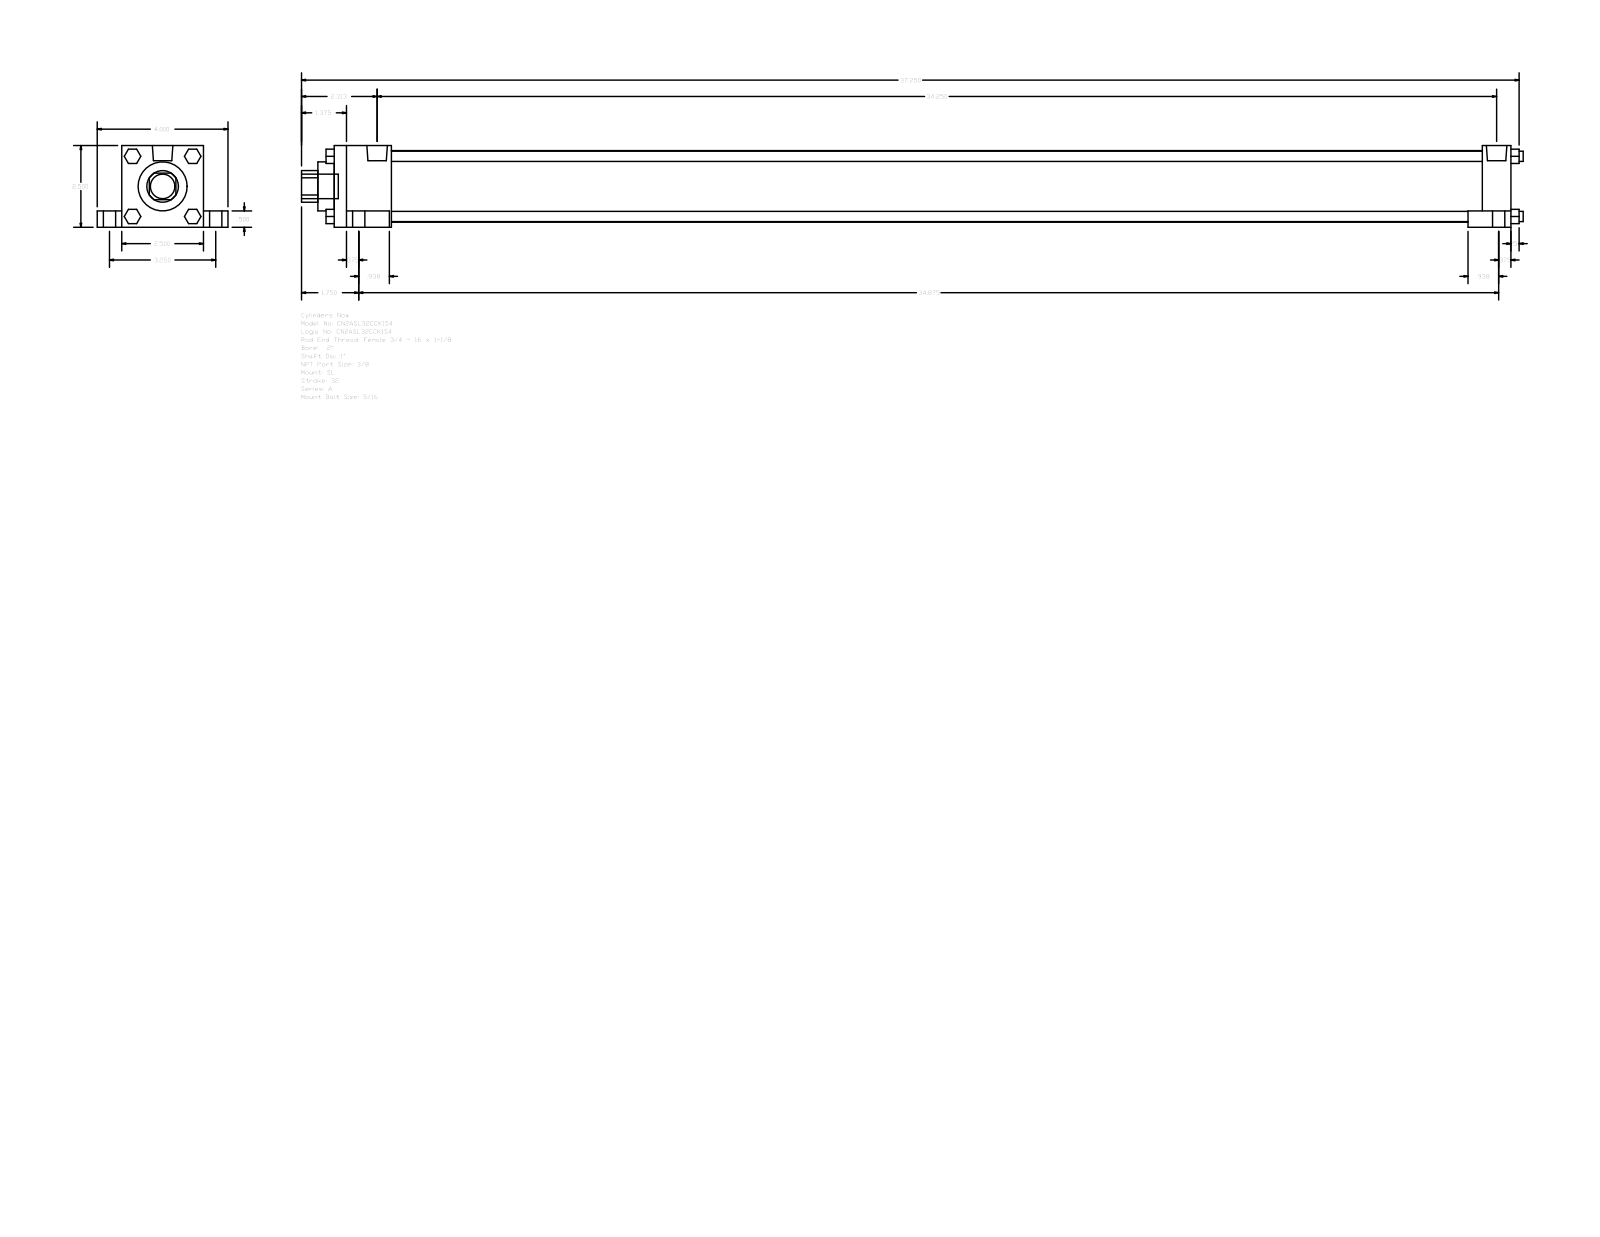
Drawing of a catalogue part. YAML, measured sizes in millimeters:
part_name: "A_SL__0200_1"
step_written_by: "GSSL Pune (CONFIG_CONTROL_DESIGN)"
units: millimeters
bodies: {solids: 0, faces: 148, planar: 112, cylindrical: 36, other: 0}
overall_size: [949.33, 101.6, 63.5]
round_holes:
  - {diameter: 25.4, count: 1}
  - {diameter: 38.1, count: 1}
  - {diameter: 55.63, count: 1}
round_bosses_or_shafts:
  - {diameter: 15.88, count: 4}
  - {diameter: 9.53, count: 4}
  - {diameter: 7.94, count: 4}
  - {diameter: 5.56, count: 4}
  - {diameter: 15.93, count: 2}
  - {diameter: 19.05, count: 1}
partial_cylinders:
  - {radius: 12.29, count: 1}
face_to_face_distances: [63.5, 12.7, 914.4, 50.8, 22.22, 19.05, 82.55, 44.45, 869.95, 892.18]
